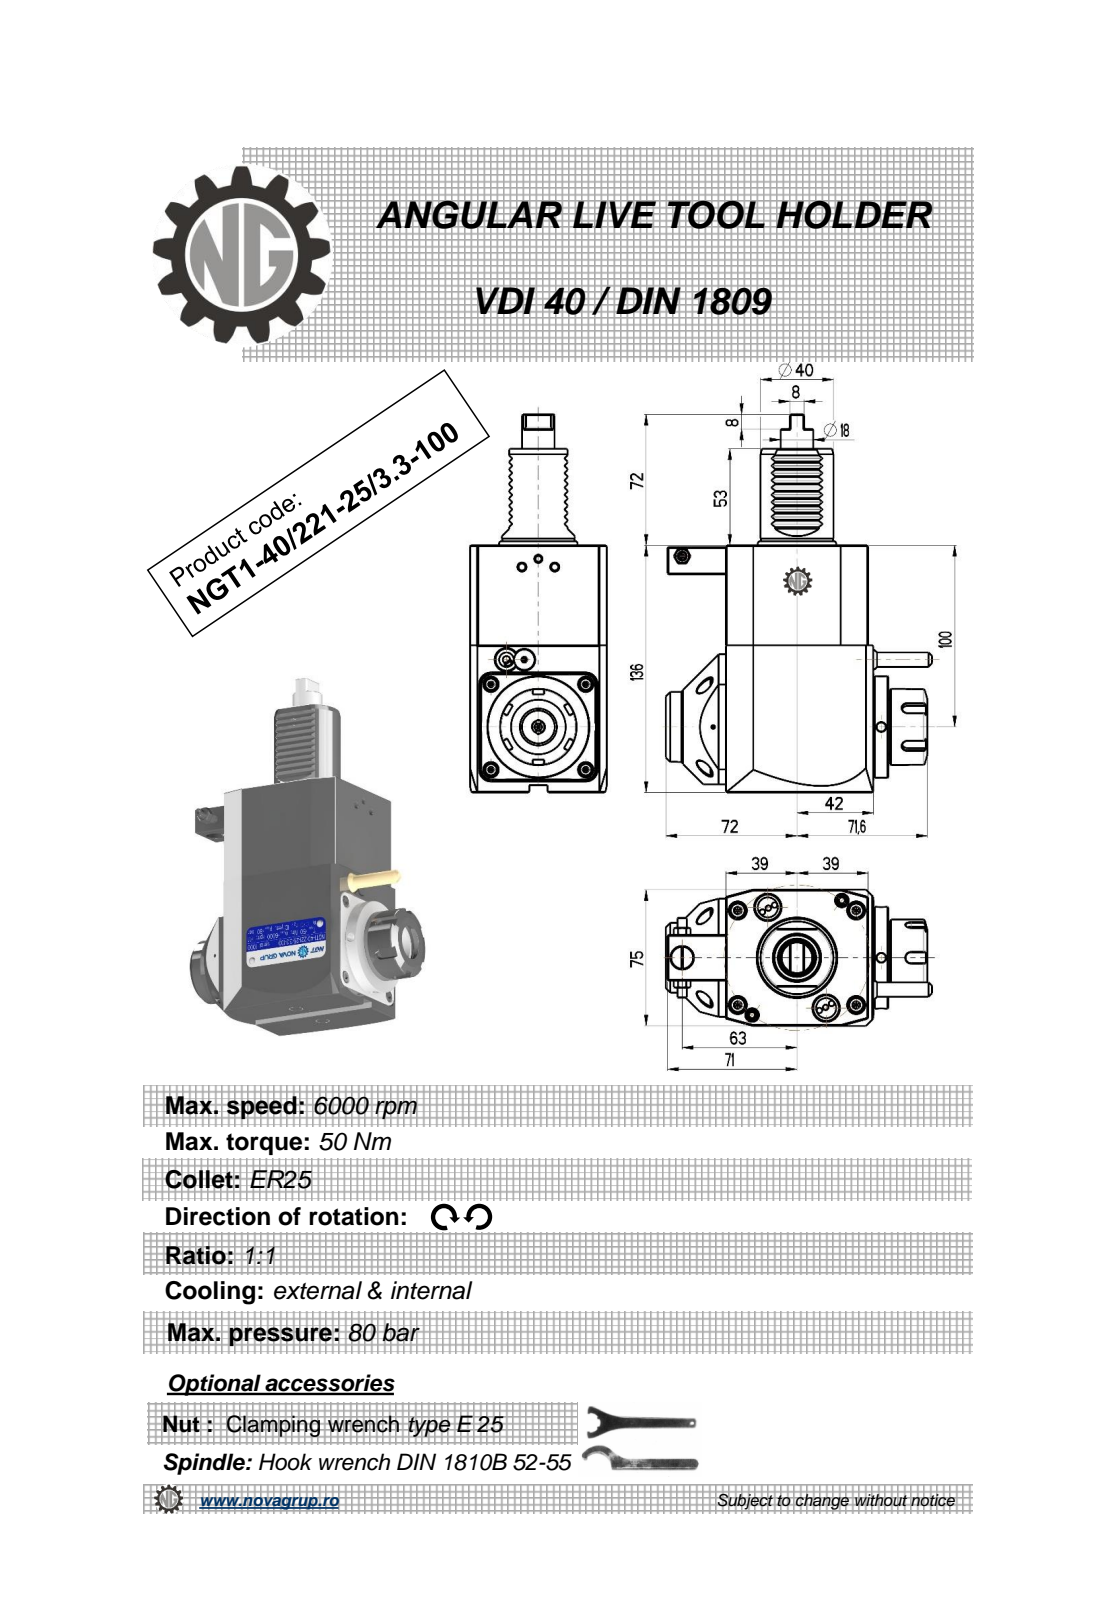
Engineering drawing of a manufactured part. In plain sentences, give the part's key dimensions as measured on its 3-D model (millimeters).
The part is named "NGT1_40_221_25_3_3_100". Its 3-D file was written by "PRO/ENGINEER BY PARAMETRIC TECHNOLOGY CORPORATION, 2010280 (CONFIG_CONTROL_DESIGN)". It is 1 solid with 476 faces: 227 planar, 98 cylindrical and 151 other. Overall it measures 208 by 146.14 by 75 millimeters. Its volume is 997 414 cubic millimeters and its surface area 77 602 square millimeters. Round holes: 3 of diameter 5, 1 of diameter 3, 1 of diameter 4.2, 1 of diameter 9.5, 1 of diameter 12, 1 of diameter 20.3. Round bosses or shafts: 1 of diameter 56, 1 of diameter 43, 1 of diameter 42, 1 of diameter 40, 1 of diameter 38.5, 1 of diameter 33, 1 of diameter 17.8, 1 of diameter 11.2. Partial cylindrical surfaces (rounded edges, fillets, slot ends): 20 of radius 0.3, 12 of radius 0.26, 6 of radius 0.22, 5 of radius 3, 2 of radius 0.8, 1 of radius 40, 1 of radius 49.79. The main face-to-face distances are 75, 136, 78, 81, 3, 11, 8, 84.88, 8.2, 80.8. The hole center spacings are 40.93, 58.19, 92.5, 109.25, 144.12.
